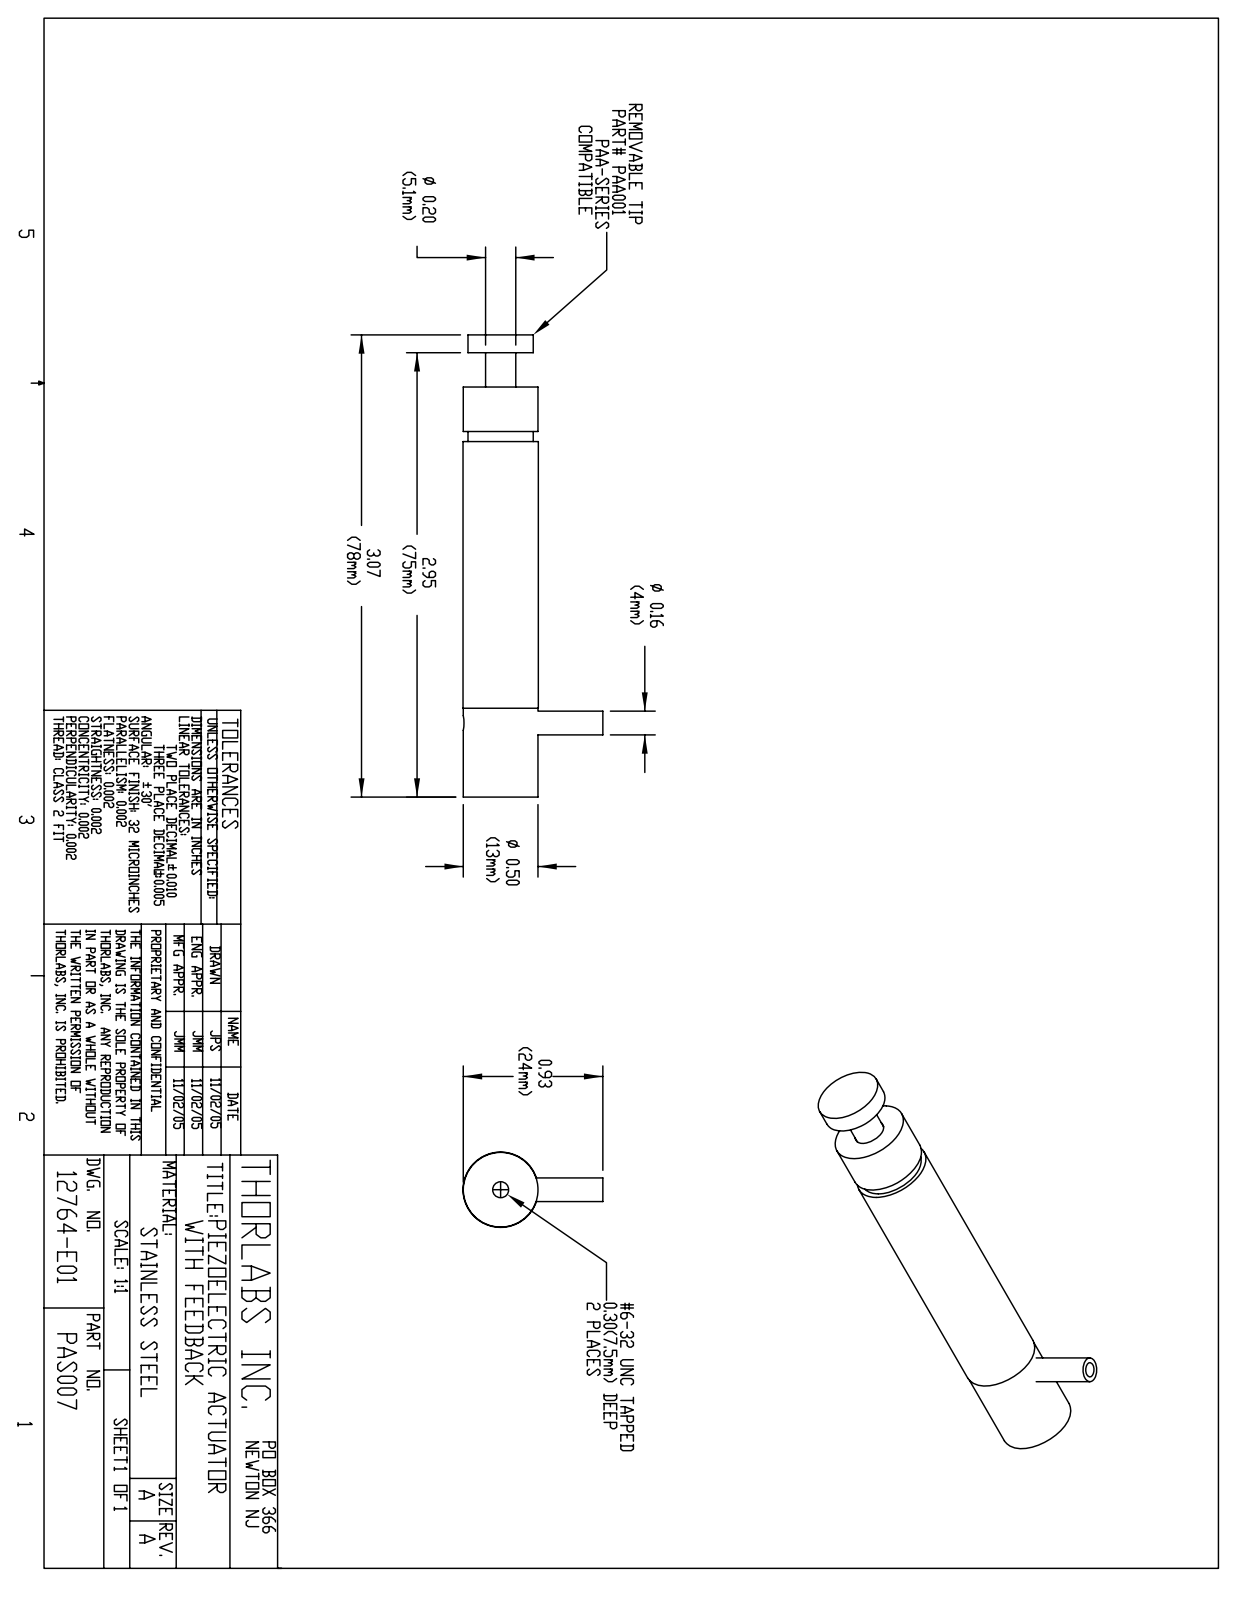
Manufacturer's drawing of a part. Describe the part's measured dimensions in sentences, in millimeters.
The part is named "12764-E0W". Its 3-D file was written by "SolidWorks 2007 (AUTOMOTIVE_DESIGN)". It is 0 solids with 39 faces: 11 planar, 28 cylindrical and 0 other. Overall it measures 78 by 23.6 by 12.7 millimeters. Round holes: 2 of diameter 2.5, 1 of diameter 2.4, 1 of diameter 2.7, 1 of diameter 5.3, 1 of diameter 9.6, 1 of diameter 11.4. Round bosses or shafts: 1 of diameter 12.7, 1 of diameter 12.6, 1 of diameter 11, 1 of diameter 5.1, 1 of diameter 4. The main face-to-face distances are 69.2, 8.8, 78, 3, 5.8, 75, 15, 60, 68, 65.
